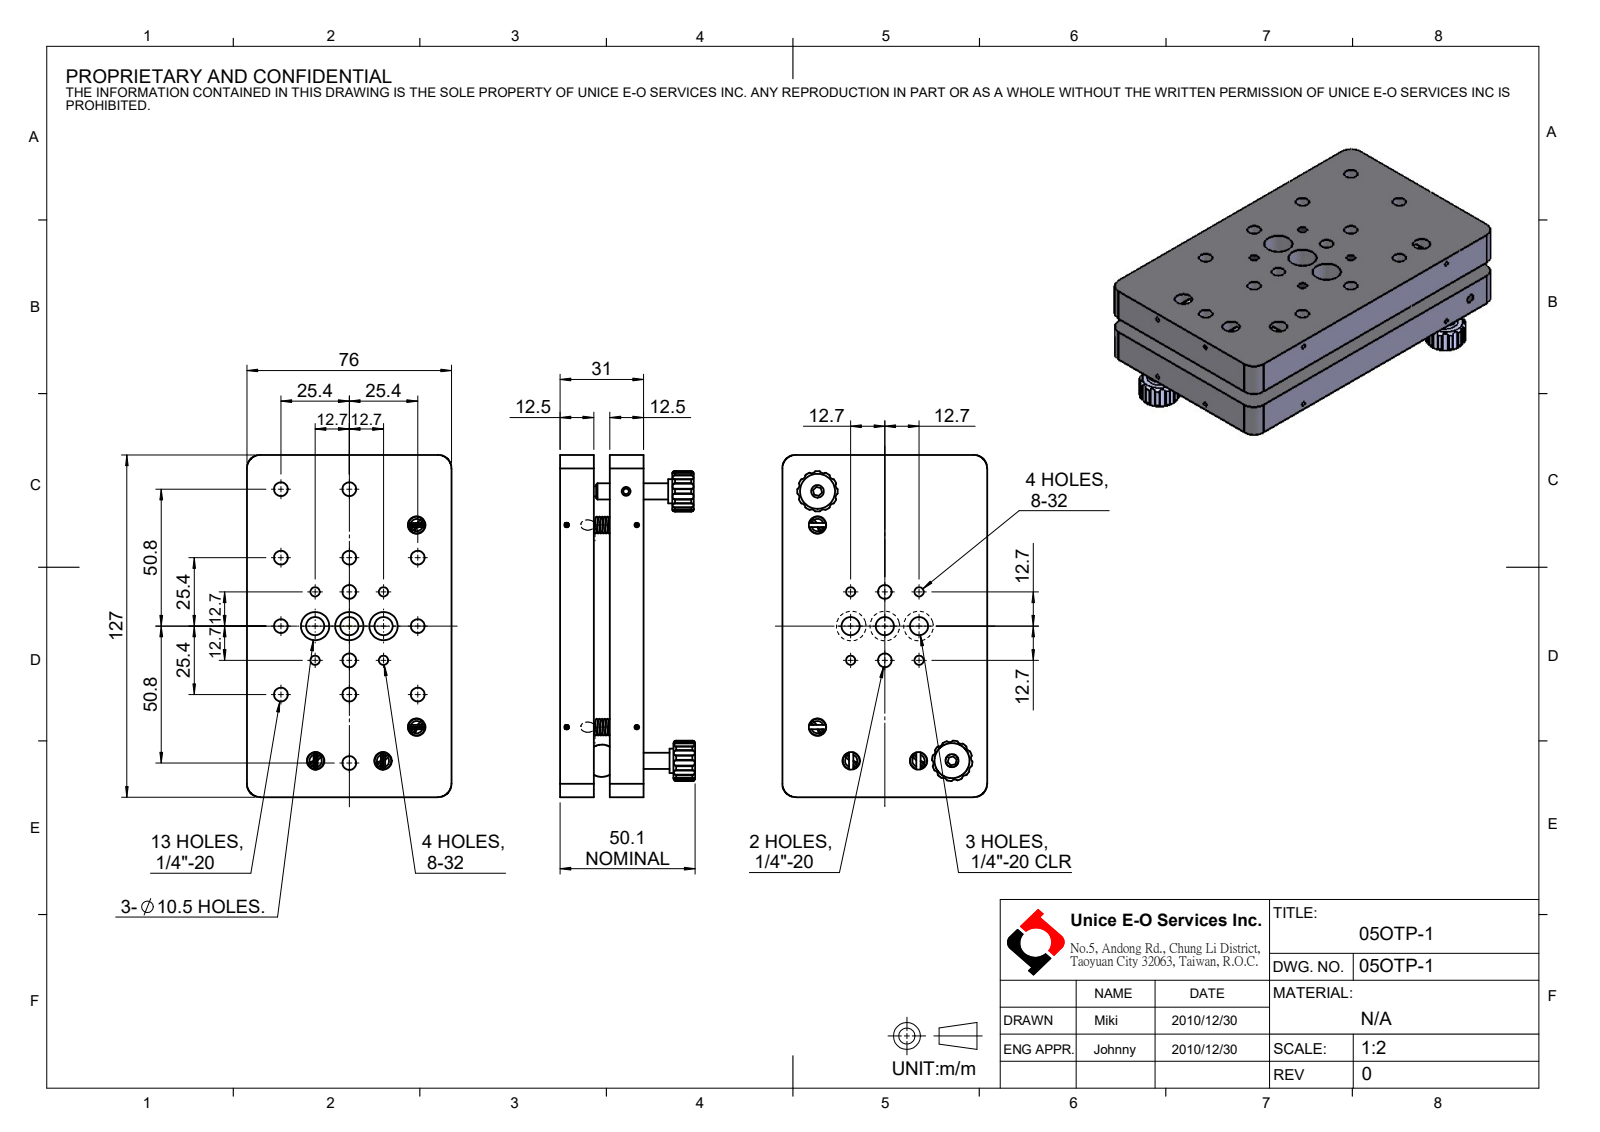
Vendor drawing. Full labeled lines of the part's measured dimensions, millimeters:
Part name (STEP PRODUCT): 05OTP-1
STEP written by: SolidWorks 2016 (CONFIG_CONTROL_DESIGN)
Units: millimetres
Bodies: 28 solids, 584 faces (127 planar, 329 cylindrical, 128 other)
Overall size (bounding box): 127 × 76 × 50.13
Volume: 231 022 mm³ · Surface area: 63 959 mm²
Round holes (diameter × count): ⌀5.11 ×13, ⌀1.2 ×8, ⌀1.7 ×8, ⌀3.45 ×4, ⌀6.5 ×4, ⌀6.76 ×3, ⌀10.5 ×3, ⌀11.51 ×3, ⌀3.3 ×2, ⌀4 ×2, ⌀4.7 ×2, ⌀5.9 ×2
Round bosses / shafts (diameter × count): ⌀1.6 ×8, ⌀0.8 ×4, ⌀10 ×2, ⌀9 ×2, ⌀4 ×2, ⌀1.5 ×2
Partial cylindrical surfaces — rounded edges, fillets, slot ends (radius × count): R0.3 ×48, R1.5 ×25, R0.75 ×4, R5 ×4, R7.5 ×2
Main face-to-face distances: 12.5, 18.5, 31, 6, 76, 127, 0.47, 6.48, 6.02, 12.02
Hole centre spacings: 28.4, 25.4, 40.16, 17.96, 12.7, 35.92, 56.8, 45.79
